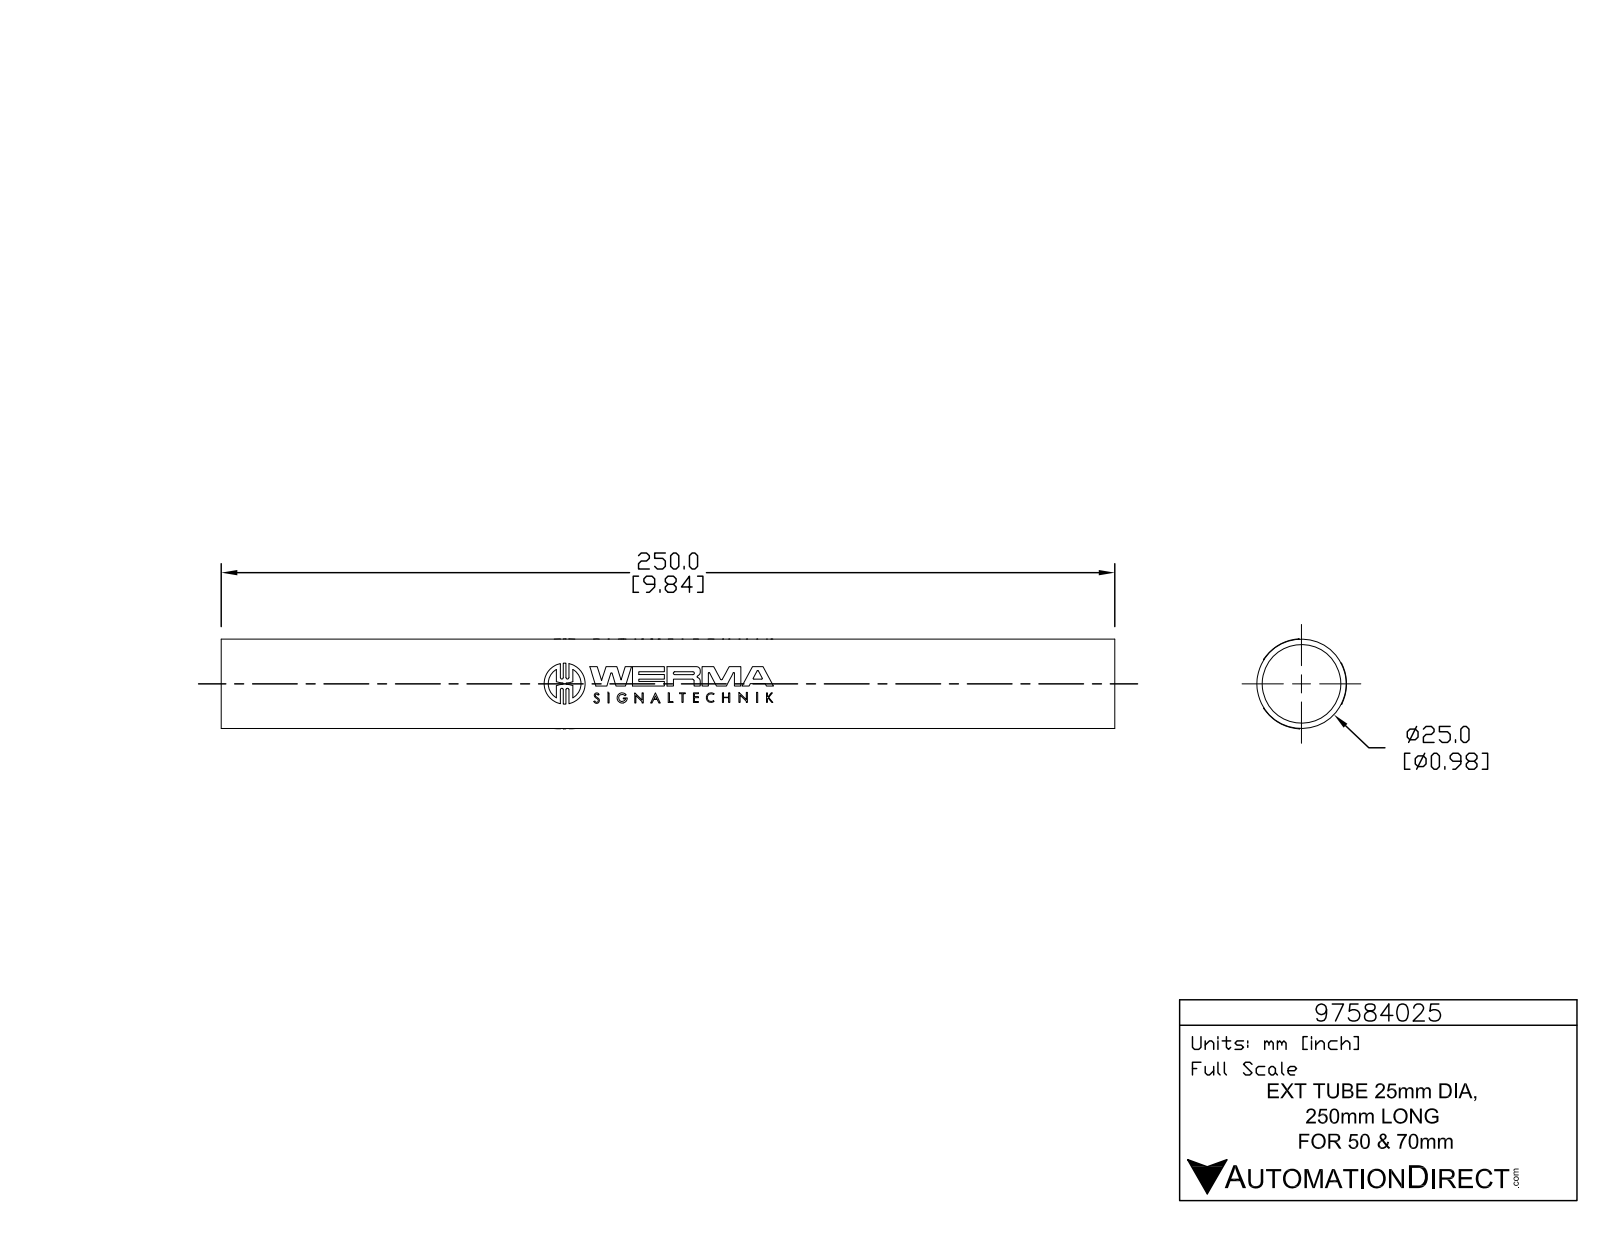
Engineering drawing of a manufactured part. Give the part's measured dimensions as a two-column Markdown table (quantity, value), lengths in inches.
| quantity | value |
| --- | --- |
| part name | 97584025 |
| STEP written by | SolidWorks 2015 (AUTOMOTIVE_DESIGN) |
| units | inches |
| bodies | 1 solid, 752 faces (521 planar, 231 cylindrical, 0 other) |
| overall size | 9.843 × 0.991 × 0.988 |
| volume | 1.694 in³ |
| surface area | 57.8 in² |
| round holes (diameter × count) | 0.078 × 3, 0.866 × 1 |
| round bosses / shafts (diameter × count) | 0.452 × 3, 0.113 × 3, 0.984 × 1 |
| partial cylindrical surfaces (radius × count) | 0.007 × 9, 0.007 × 6, 0.016 × 6, 0.016 × 6, 0.016 × 6, 0.262 × 6, 0.006 × 3, 0.006 × 3 |
| main face-to-face distances | 9.843, 0.213, 0.075, 0.033, 0.061, 0.138, 0.05, 0.031, 0.182, 0.232 |
